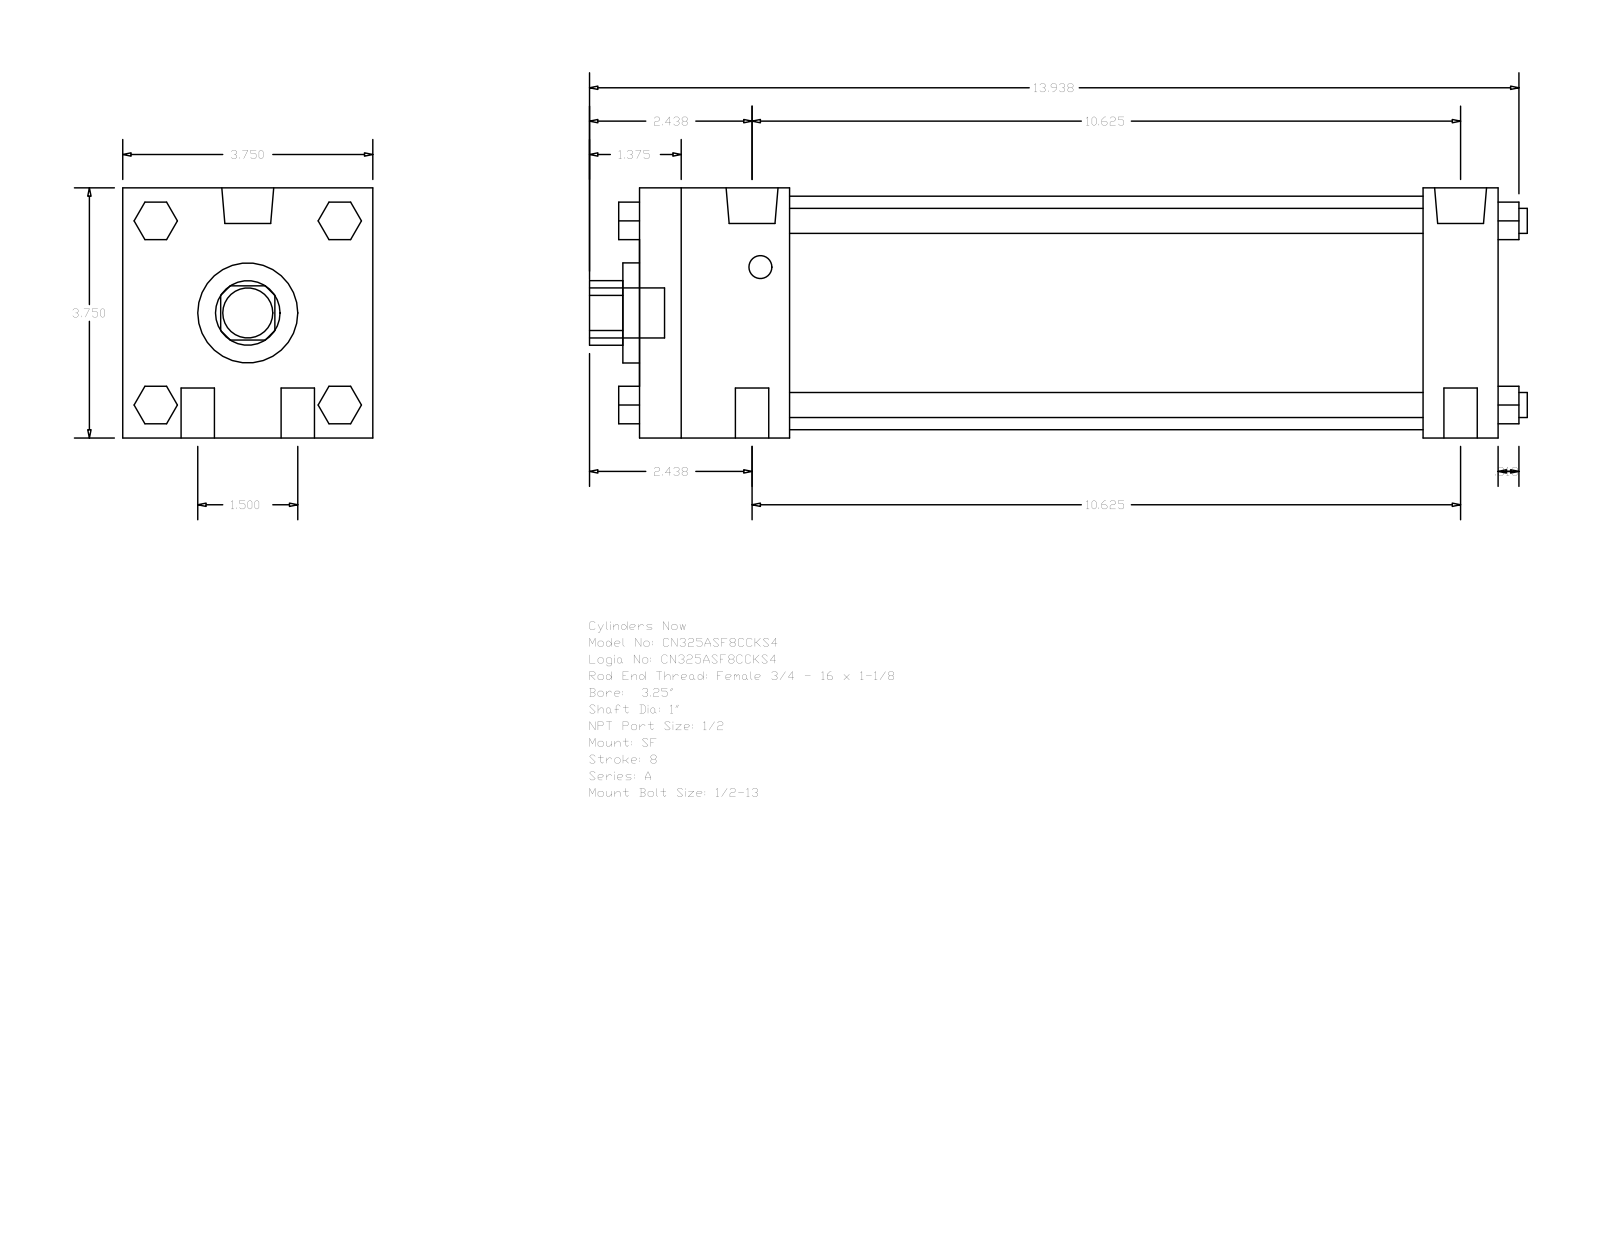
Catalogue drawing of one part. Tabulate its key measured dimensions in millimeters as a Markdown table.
| quantity | value |
| --- | --- |
| part name | A_SF__0325_1 |
| STEP written by | GSSL Pune (CONFIG_CONTROL_DESIGN) |
| units | millimeters |
| bodies | 0 solids, 124 faces (94 planar, 30 cylindrical, 0 other) |
| overall size | 357.19 × 95.25 × 95.25 |
| round holes (diameter × count) | 25.4 × 1, 38.1 × 1, 88.9 × 1 |
| round bosses / shafts (diameter × count) | 12.7 × 4, 9.53 × 4, 19.77 × 2, 8.73 × 2, 19.05 × 1 |
| partial cylindrical surfaces (radius × count) | 12.29 × 1 |
| main face-to-face distances | 95.24, 327.02, 28.57, 298.45, 57.15, 241.3, 269.87, 14.28, 35.05, 60.71 |
